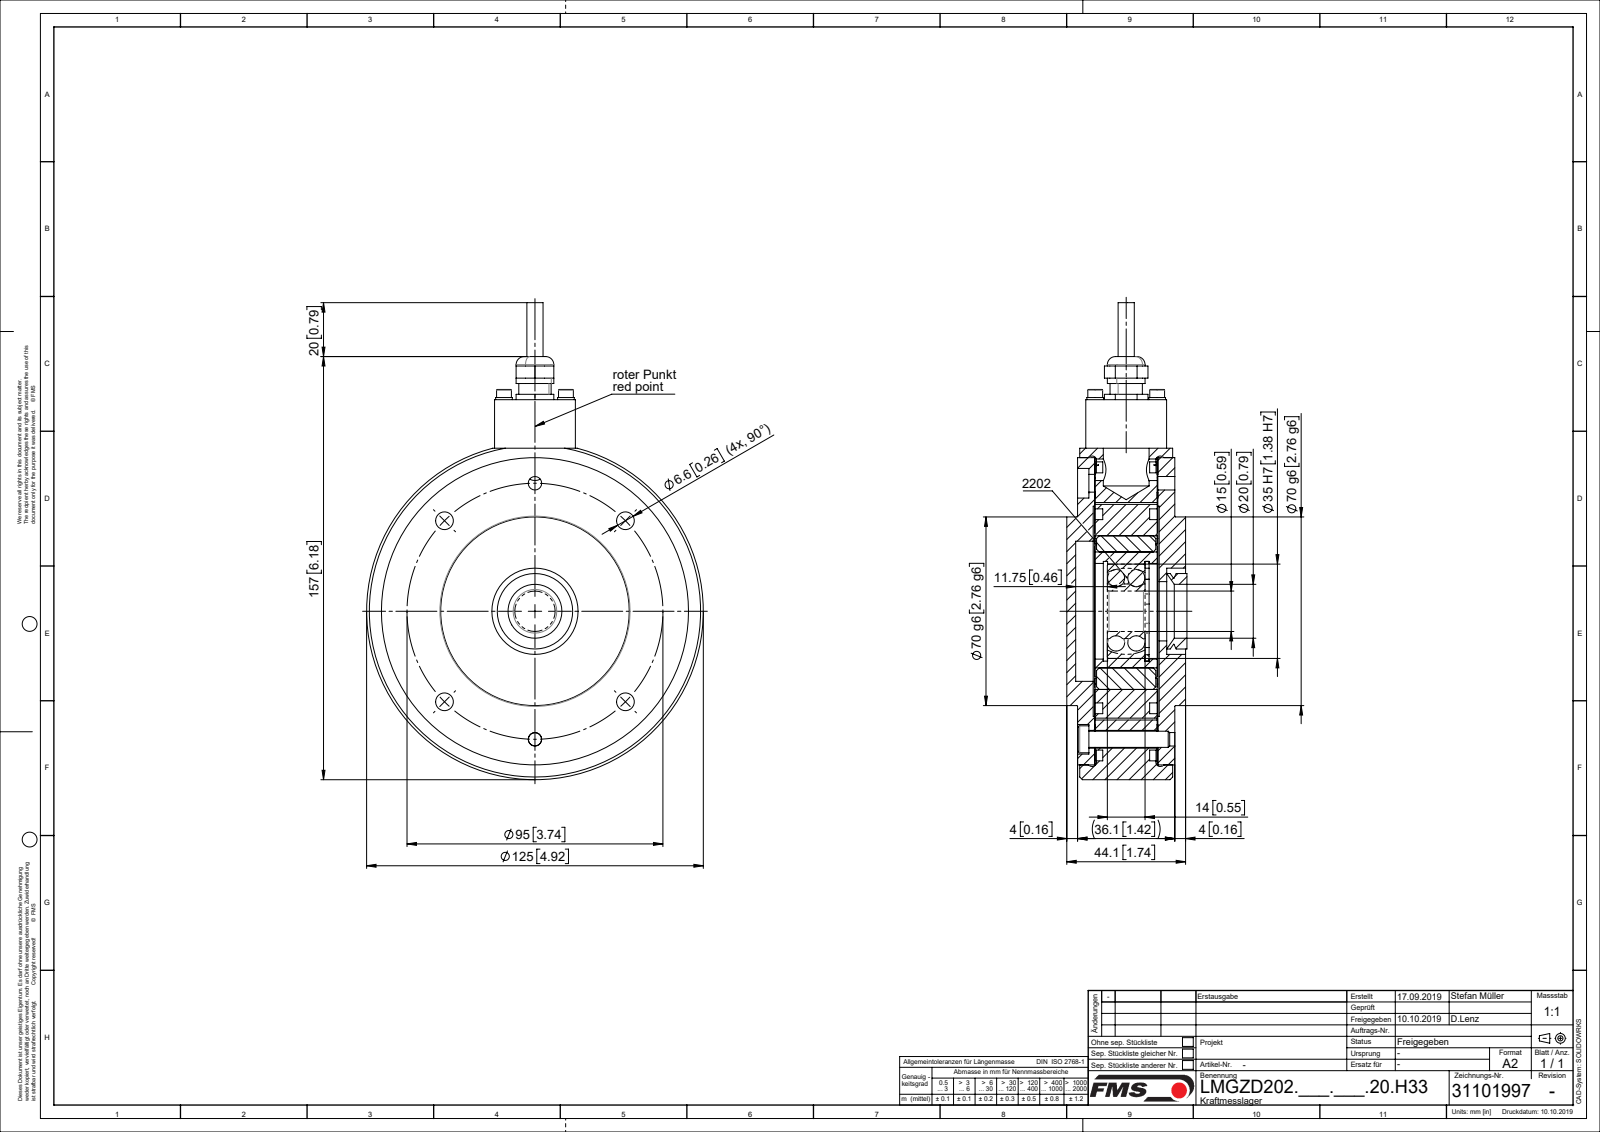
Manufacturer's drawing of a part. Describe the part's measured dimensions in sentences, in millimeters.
The part is named "31101749_01; Zyl-Schr DIN7984_M6x30; 49046-04_stp_01; Si-Ring DIN472_D35x1.5 (+8 more)". Its 3-D file was written by "SolidWorks 2018 (CONFIG_CONTROL_DESIGN)". It is 41 solids with 572 faces: 158 planar, 296 cylindrical and 118 other. Overall it measures 177 by 125 by 44.6 millimeters. Its volume is 418 057 cubic millimeters and its surface area 139 936 square millimeters. Round holes: 6 of diameter 2.5, 6 of diameter 6.6, 4 of diameter 3.1, 4 of diameter 3.4, 4 of diameter 6.8, 2 of diameter 5, 2 of diameter 6, 2 of diameter 8, 2 of diameter 11, 1 of diameter 11.5, 1 of diameter 15, 1 of diameter 17. Round bosses or shafts: 4 of diameter 6.2, 4 of diameter 5.5, 4 of diameter 3, 1 of diameter 125, 1 of diameter 114, 1 of diameter 103, 1 of diameter 70, 1 of diameter 68. Partial cylindrical surfaces (rounded edges, fillets, slot ends): 8 of radius 5, 4 of radius 0.1, 4 of radius 9, 2 of radius 3.58, 1 of radius 13.1, 1 of radius 16.07, 1 of radius 24.82, 1 of radius 25.18. The main face-to-face distances are 23.25, 6.3, 6.55, 29.55, 29.8, 23, 23.5, 23.75, 4, 33.8. The hole center spacings are 47.5, 16.26, 23, 34.67, 36.36, 67.18, 67.54, 87.77.
